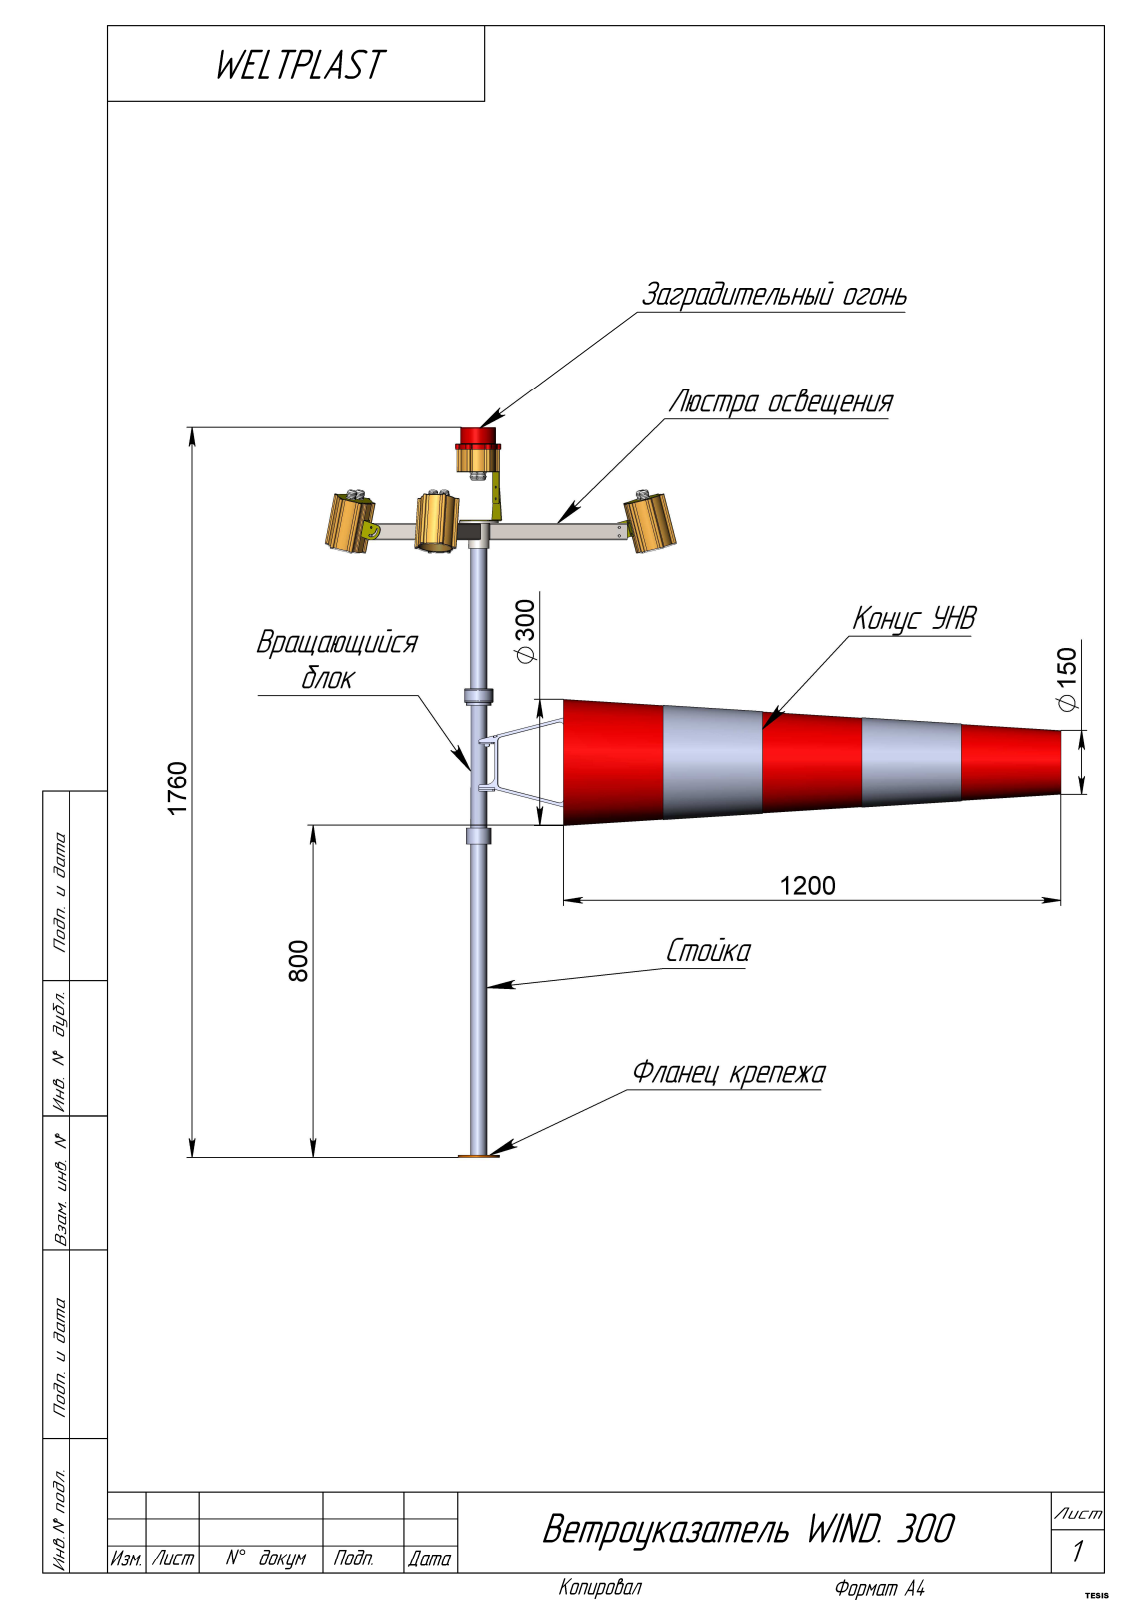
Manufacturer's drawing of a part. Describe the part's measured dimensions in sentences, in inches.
The part is named "Нижняя Крышка; Фланец верх.; WIND.033 (кольцо 112мм); Сборка верх. секции (+8 more)". Its 3-D file was written by "SolidWorks 2017 (AUTOMOTIVE_DESIGN)". It is 62 solids with 1916 faces: 511 planar, 1218 cylindrical and 187 other. Overall it measures 69.898 by 69.173 by 32.91 inches. Its volume is 201.6 cubic inches and its surface area 4 971 square inches. Round holes: 42 of diameter 0.173, 23 of diameter 0.236, 8 of diameter 0.496, 8 of diameter 0.797, 6 of diameter 0.177, 6 of diameter 0.197, 6 of diameter 0.252, 4 of diameter 0.433, 4 of diameter 3.11, 2 of diameter 0.157, 2 of diameter 0.165, 2 of diameter 0.331. Round bosses or shafts: 8 of diameter 0.846, 8 of diameter 0.776, 4 of diameter 0.315, 1 of diameter 3.937, 1 of diameter 3.74, 1 of diameter 3.346, 1 of diameter 2.756, 1 of diameter 2.362. Partial cylindrical surfaces (rounded edges, fillets, slot ends): 98 of radius 0.197, 52 of radius 0.157, 20 of radius 0.079, 18 of radius 0.177, 14 of radius 0.059, 12 of radius 0.02, 12 of radius 0.098, 12 of radius 0.118. The main face-to-face distances are 0.079, 0.709, 0.118, 1.496, 0.708, 0.787, 0.63, 0.051, 0.157, 1.575. The hole center spacings are 1.87, 3.239, 3.239, 3.74, 1.665, 2.198, 1.102, 1.319.
